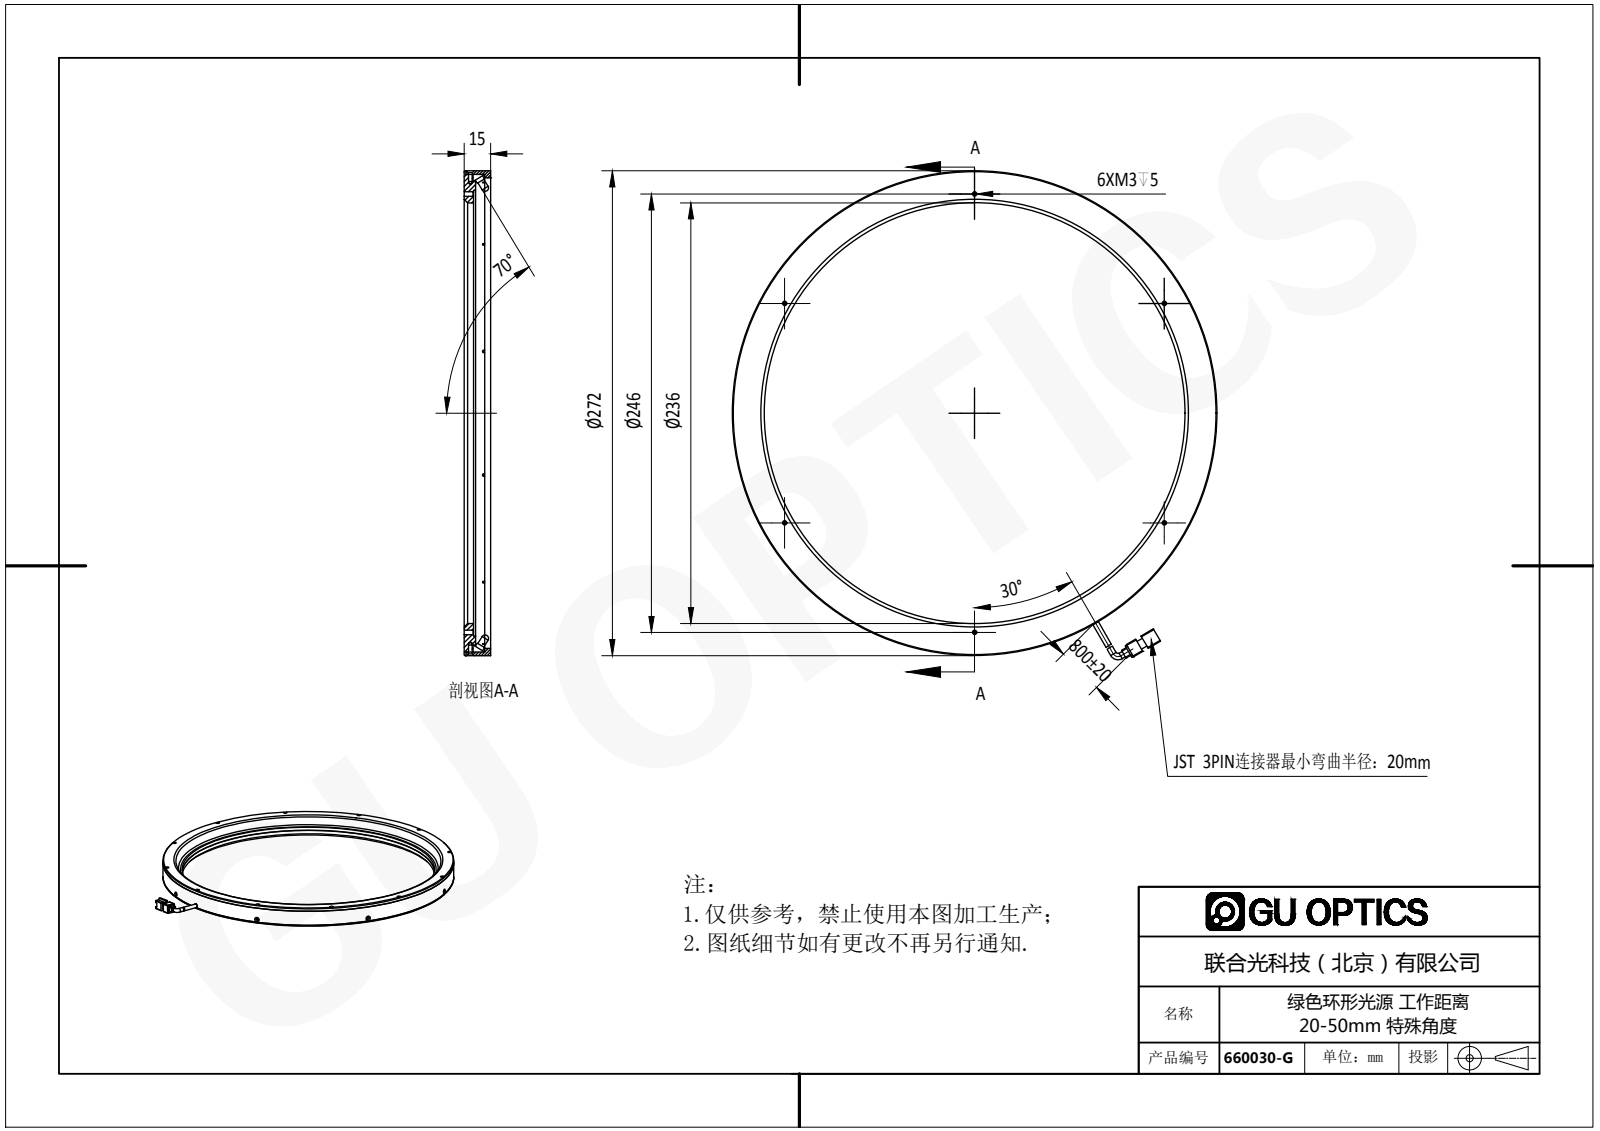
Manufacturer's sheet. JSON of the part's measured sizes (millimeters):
{"part_name": "660030-G", "step_written_by": "SolidWorks 2016 (AUTOMOTIVE_DESIGN)", "units": "millimeters", "bodies": {"solids": 156, "faces": 2958, "planar": 1895, "cylindrical": 793, "other": 270}, "overall_size": [274.35, 272, 19.24], "volume_mm3": 168197, "surface_area_mm2": 140450, "round_holes": [[1.6, 18], [1.25, 12], [1.7, 12], [2, 6], [2.4, 6], [2.5, 6], [3.5, 1], [236, 1], [250, 1], [264, 1]], "round_bosses_or_shafts": [[3.8, 150], [3, 150], [3.5, 2], [272, 1], [268, 1], [260, 1]], "partial_cylinders_radius": [[0.5, 8], [1, 4], [1.6, 1], [3, 1]], "face_to_face_distances": [14.94, 3, 17.94, 5.3, 9.64, 12.64, 6.5, 8.44, 1, 1.2], "hole_center_spacings": [134, 34.98, 163.15, 247.6, 265.71, 69.36, 102.56, 258.87]}
